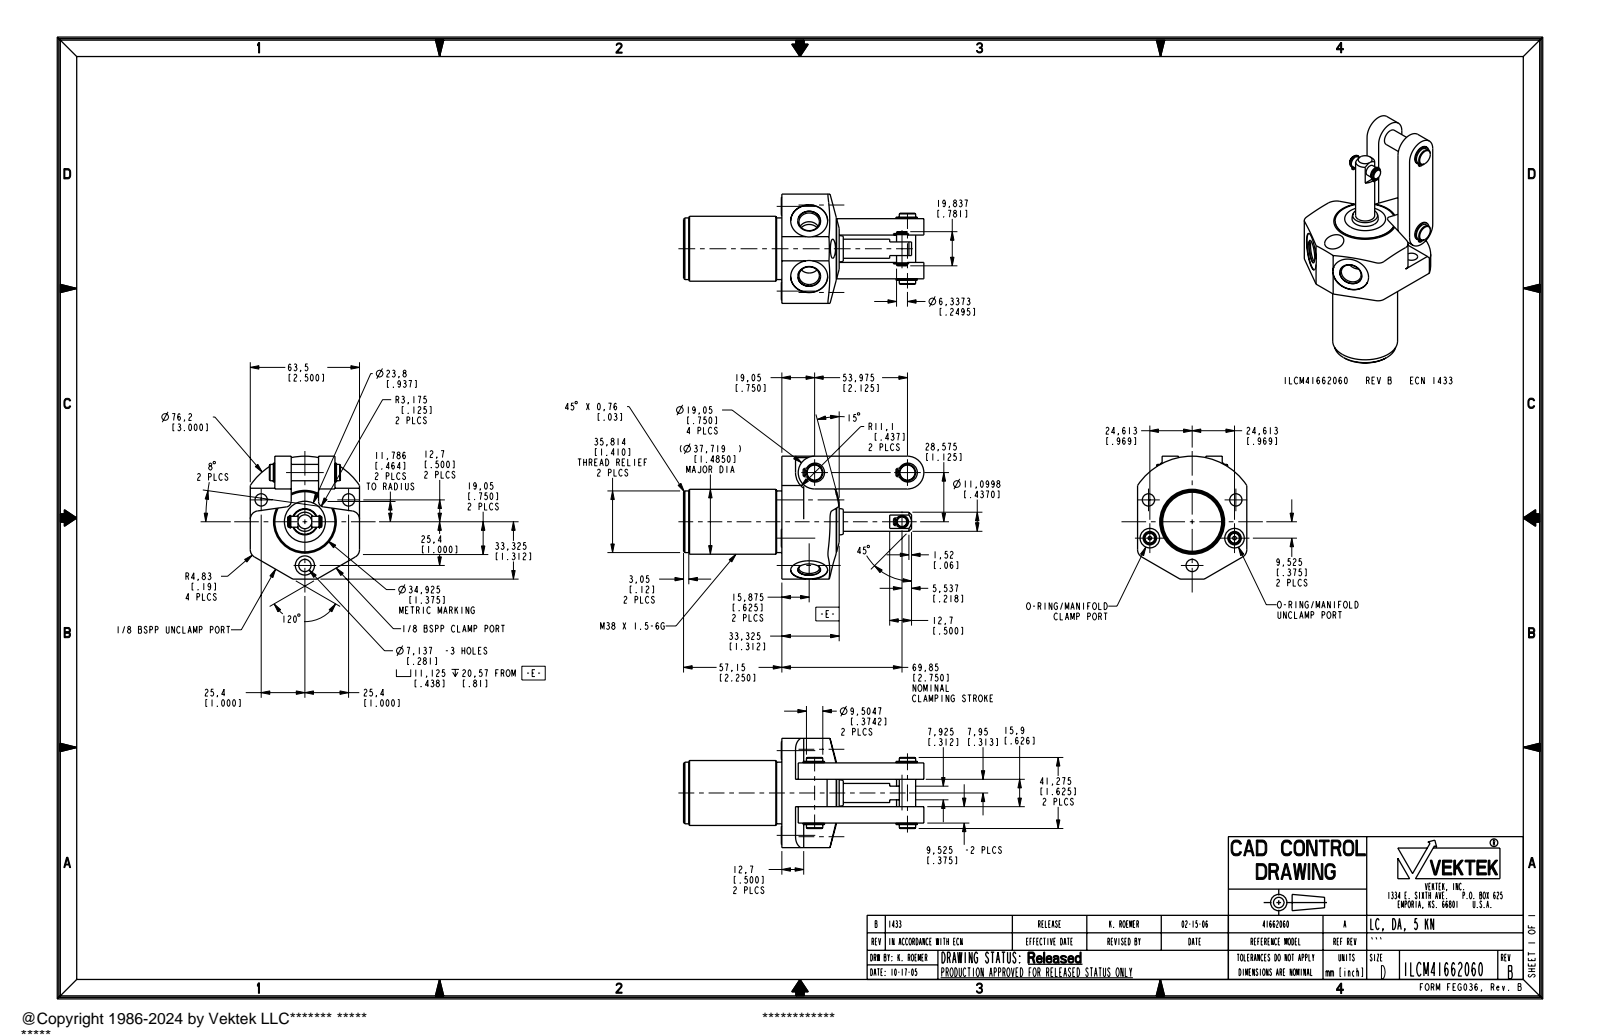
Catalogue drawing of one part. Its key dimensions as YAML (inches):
part_name: "ILCM41662060"
step_written_by: "PRO/ENGINEER BY PARAMETRIC TECHNOLOGY CORPORATION, 2004290 (AUTOMOTIVE_DESIGN_CC2)"
units: inches
bodies: {solids: 1, faces: 306, planar: 121, cylindrical: 139, other: 46}
overall_size: [5.5, 2.812, 2.5]
volume: 11.18
surface_area: 63.75
round_holes:
  - {diameter: 0.041, count: 6}
  - {diameter: 0.281, count: 3}
  - {diameter: 0.098, count: 2}
  - {diameter: 0.256, count: 2}
  - {diameter: 0.446, count: 2}
  - {diameter: 0.468, count: 2}
  - {diameter: 0.524, count: 2}
  - {diameter: 0.846, count: 2}
  - {diameter: 0.438, count: 1}
round_bosses_or_shafts:
  - {diameter: 0.518, count: 2}
  - {diameter: 0.433, count: 2}
  - {diameter: 0.374, count: 2}
  - {diameter: 0.224, count: 2}
  - {diameter: 0.118, count: 2}
  - {diameter: 1.485, count: 1}
  - {diameter: 1.431, count: 1}
  - {diameter: 1.41, count: 1}
partial_cylinders:
  - {radius: 0.041, count: 12}
  - {radius: 0.19, count: 4}
  - {radius: 0.06, count: 2}
  - {radius: 0.125, count: 2}
  - {radius: 0.375, count: 2}
  - {radius: 0.145, count: 1}
  - {radius: 0.437, count: 1}
  - {radius: 1.5, count: 1}
face_to_face_distances: [0.375, 1.001, 0.562, 0.937, 1.563, 1.938, 1.376, 0.626, 0.75, 2.25]
hole_center_spacings: [0.098, 0.876, 1.126, 1.153, 1.803, 2.125, 2.128, 2.155]
